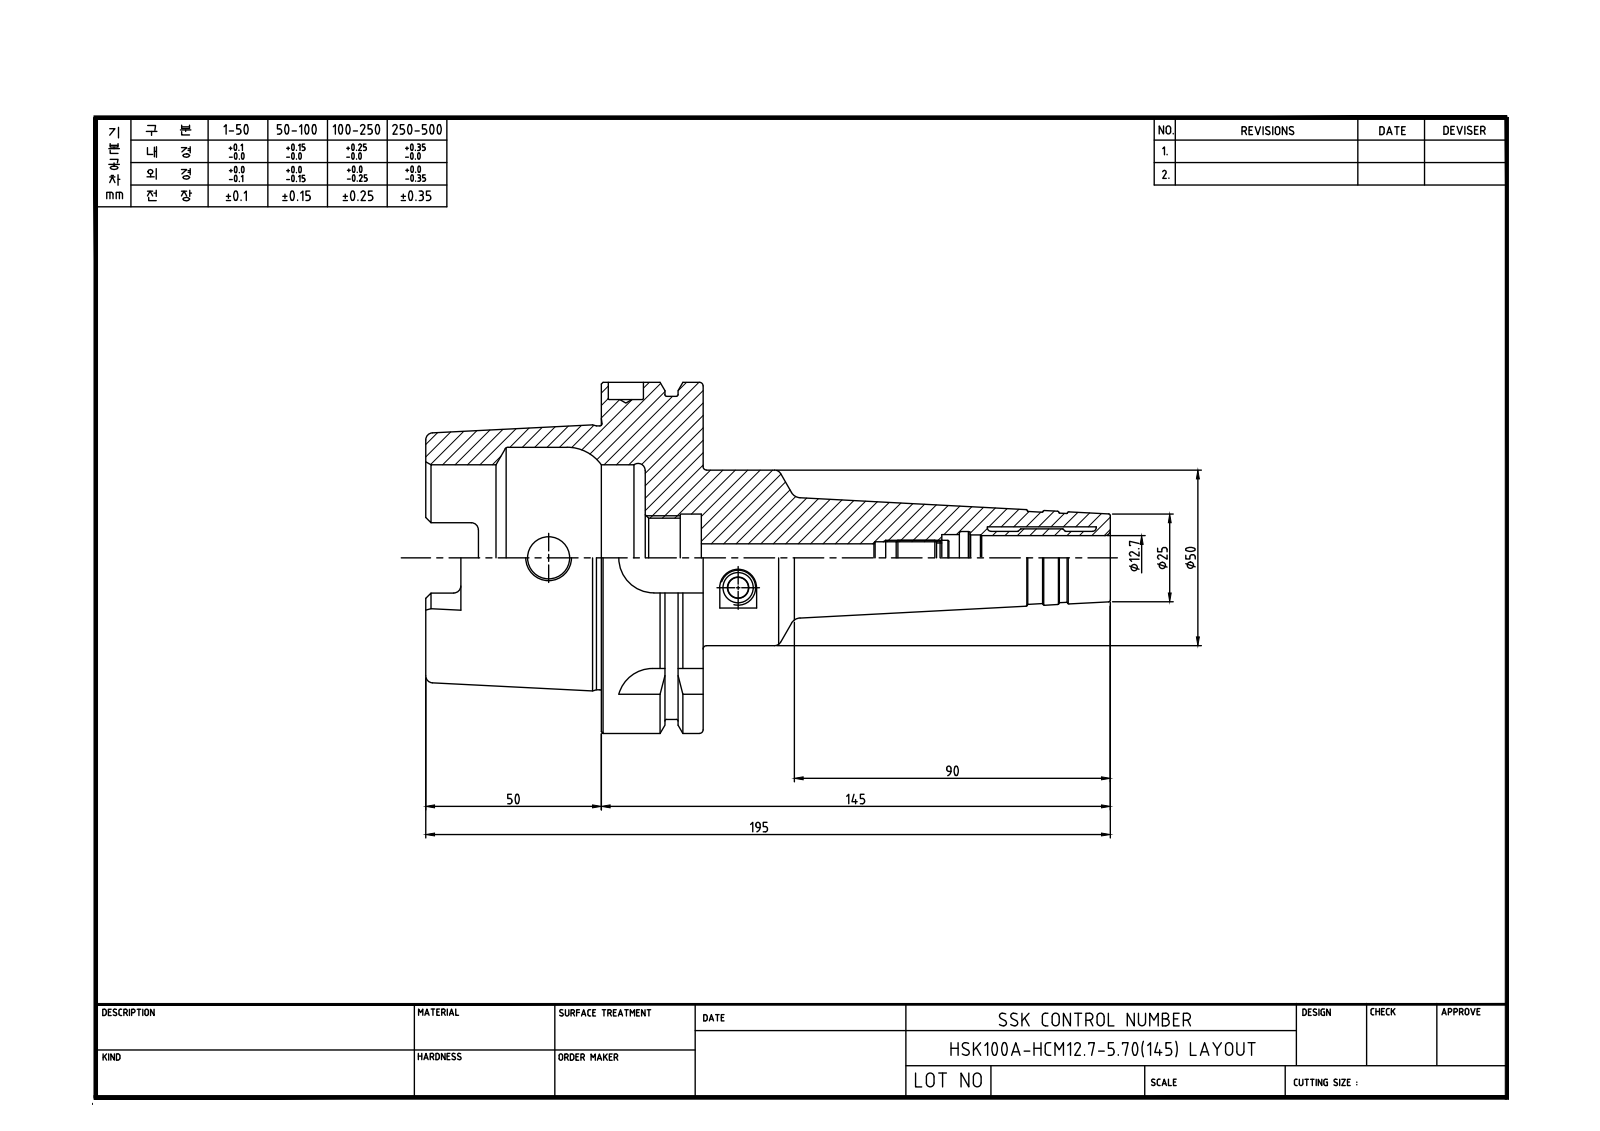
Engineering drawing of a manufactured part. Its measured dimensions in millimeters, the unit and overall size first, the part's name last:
Units: millimetres
Overall size (bounding box): 195 × 100 × 100
Round holes (diameter × count): ⌀8 ×1, ⌀8.92 ×1, ⌀10 ×1, ⌀12 ×1, ⌀12.7 ×1, ⌀13.2 ×1, ⌀22.38 ×1, ⌀25 ×1, ⌀53 ×1, ⌀63 ×1
Round bosses / shafts (diameter × count): ⌀100 ×1, ⌀92 ×1, ⌀75.41 ×1, ⌀50 ×1
Partial cylindrical surfaces — rounded edges, fillets, slot ends (radius × count): R2 ×6, R4.88 ×4, R10 ×4
Main face-to-face distances: 29, 12.5, 16.5, 62.5, 50, 79, 78.5, 28.5, 16, 0.5
Volume: 360 415 mm³ · Surface area: 65 034 mm²
Bodies: 1 solid, 134 faces (38 planar, 35 cylindrical, 61 other)
Part name (STEP PRODUCT): HSK100A-HMC12.7-145
STEP written by: Autodesk Inventor 2020 (AUTOMOTIVE_DESIGN)
